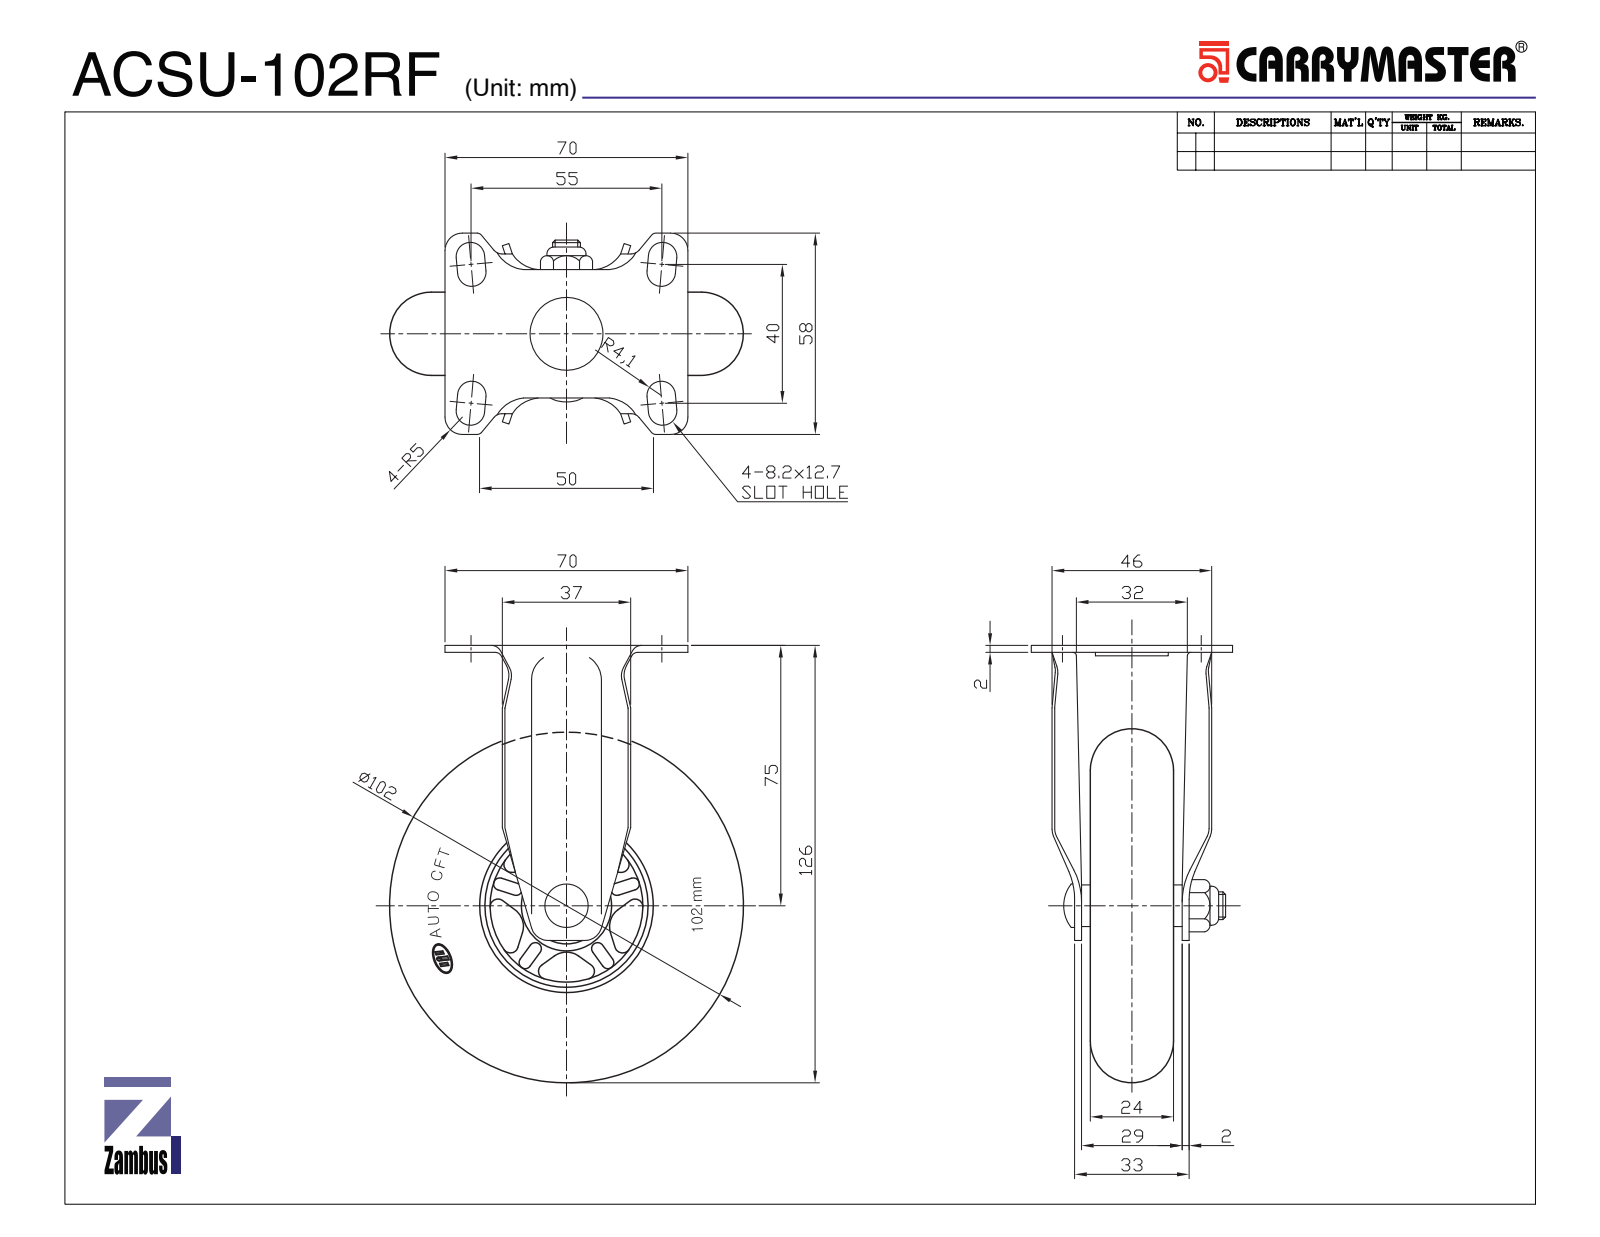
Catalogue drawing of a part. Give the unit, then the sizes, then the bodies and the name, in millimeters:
Units: millimetres
Overall size (bounding box): 126.5 × 102 × 57.8
Round holes (diameter × count): ⌀6.8 ×1, ⌀8 ×1, ⌀18 ×1, ⌀18.5 ×1, ⌀22 ×1, ⌀50 ×1
Round bosses / shafts (diameter × count): ⌀12.5 ×1, ⌀11.8 ×1, ⌀7.85 ×1
Partial cylindrical surfaces — rounded edges, fillets, slot ends (radius × count): R1 ×40, R1.5 ×10, R1.7 ×10, R2 ×10, R4.1 ×8, R0.5 ×6, R5 ×6, R3 ×5
Main face-to-face distances: 2, 24, 6.54, 30.54, 35.08, 4.54, 28.54, 3.5, 17, 1
Volume: 189 267 mm³ · Surface area: 68 189 mm²
Bodies: 7 solids, 433 faces (135 planar, 195 cylindrical, 103 other)
Part name (STEP PRODUCT): ACSU-102RF
STEP written by: SolidWorks 2015 (CONFIG_CONTROL_DESIGN)
